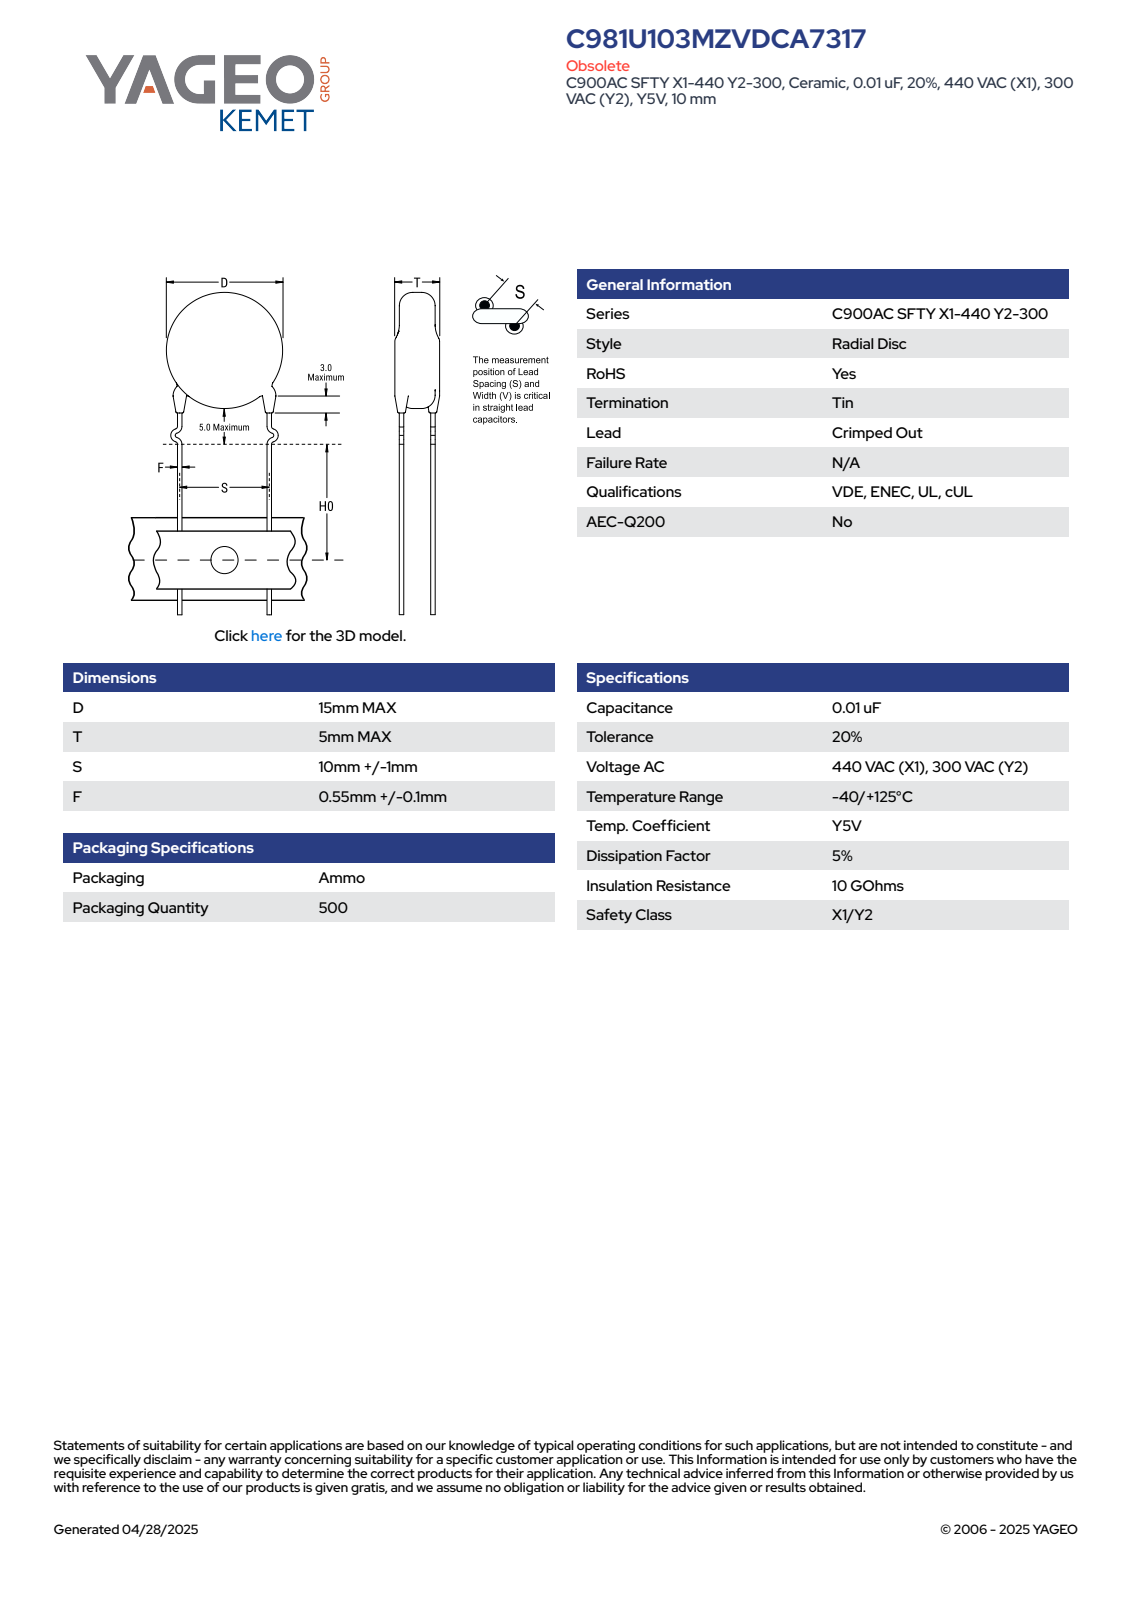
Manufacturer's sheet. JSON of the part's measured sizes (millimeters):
{"part_name": "CCD_KCOC900_D15T5S10LL20F0.55", "step_written_by": "SolidWorks 2014 (AUTOMOTIVE_DESIGN)", "units": "millimeters", "bodies": {"solids": 4, "faces": 85, "planar": 63, "cylindrical": 6, "other": 16}, "overall_size": [40, 15.21, 5], "volume_mm3": 886, "surface_area_mm2": 688, "round_bosses_or_shafts": [[1.2, 2], [15, 1]], "face_to_face_distances": [5, 8.29, 6.74, 1.55, 0.42, 0.68, 6.37, 1.26, 0.97, 0.58]}
